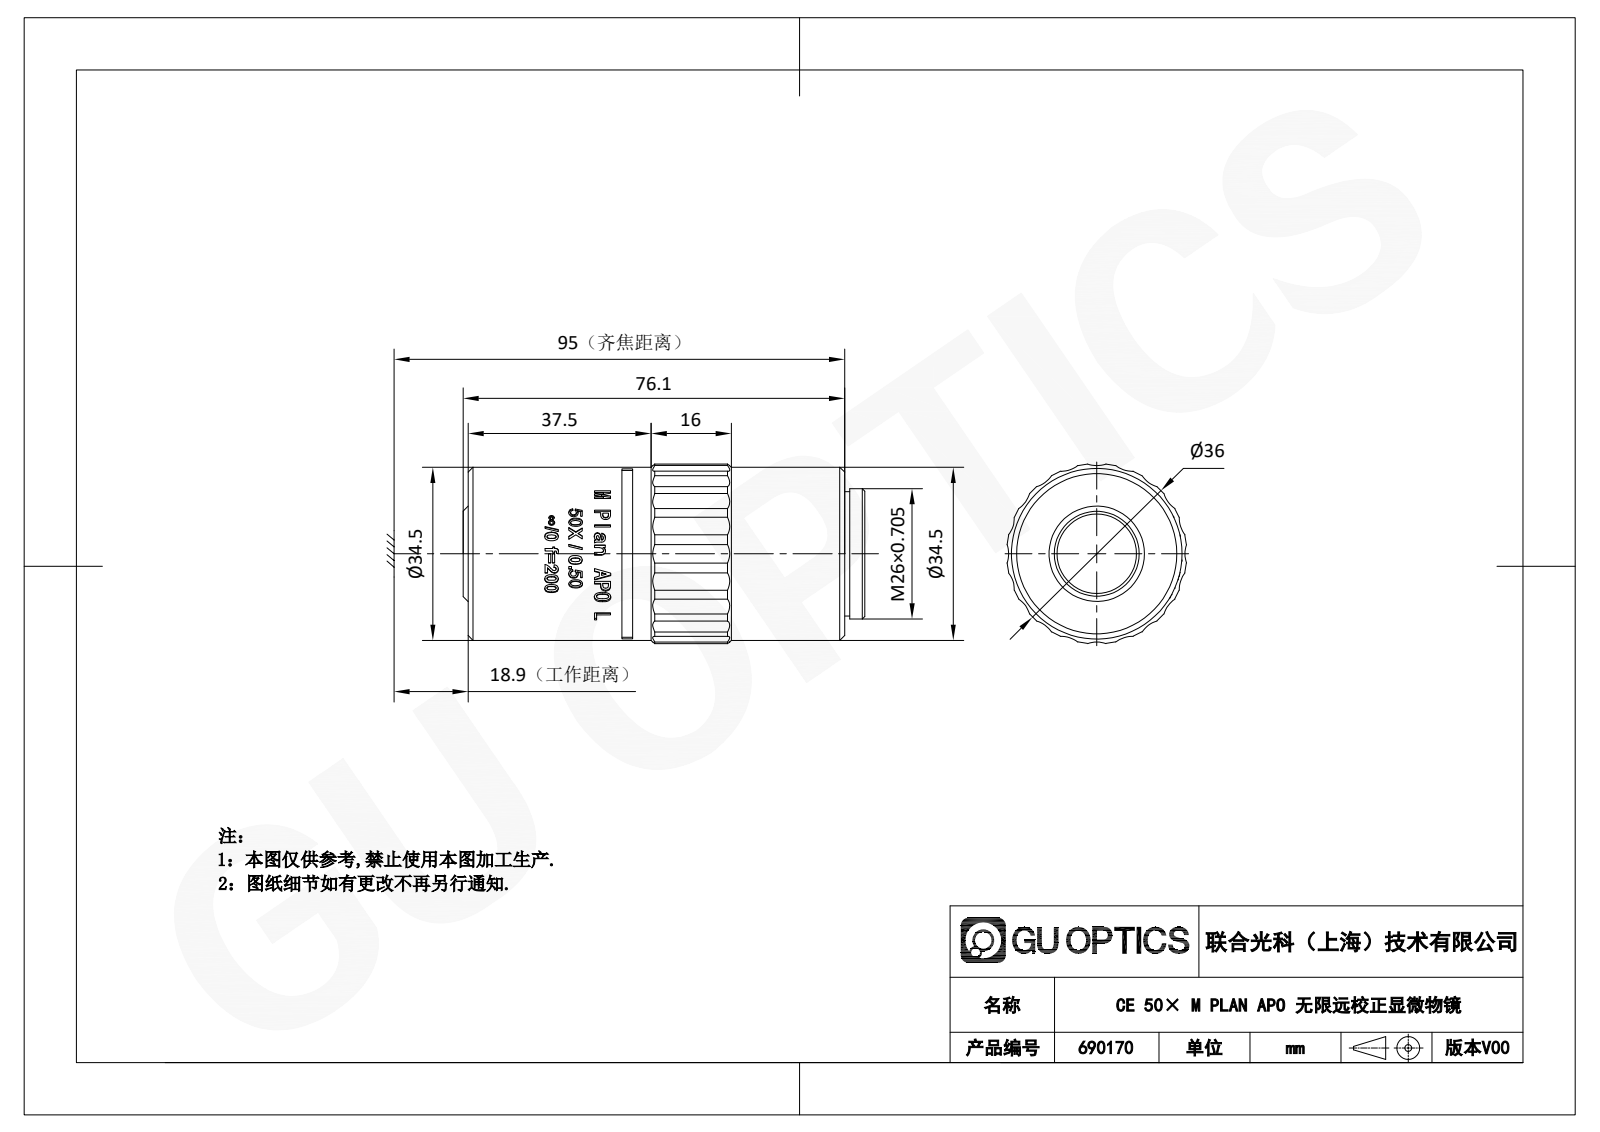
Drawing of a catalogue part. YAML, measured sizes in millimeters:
part_name: "690167"
step_written_by: "SolidWorks 2020 (CONFIG_CONTROL_DESIGN)"
units: millimeters
bodies: {solids: 1, faces: 376, planar: 107, cylindrical: 96, other: 173}
overall_size: [80.11, 35.81, 35.81]
volume: 72196
surface_area: 10808
round_holes:
  - {diameter: 15, count: 1}
  - {diameter: 22, count: 1}
round_bosses_or_shafts:
  - {diameter: 34.5, count: 1}
  - {diameter: 33.88, count: 1}
  - {diameter: 26, count: 1}
  - {diameter: 24.8, count: 1}
partial_cylinders:
  - {radius: 5.29, count: 20}
  - {radius: 16.84, count: 1}
  - {radius: 17.05, count: 1}
  - {radius: 18, count: 1}
face_to_face_distances: [76.41, 1.31, 75.1, 0.5, 76.91, 75.6, 2.7, 4.01, 79.11, 79.61]
